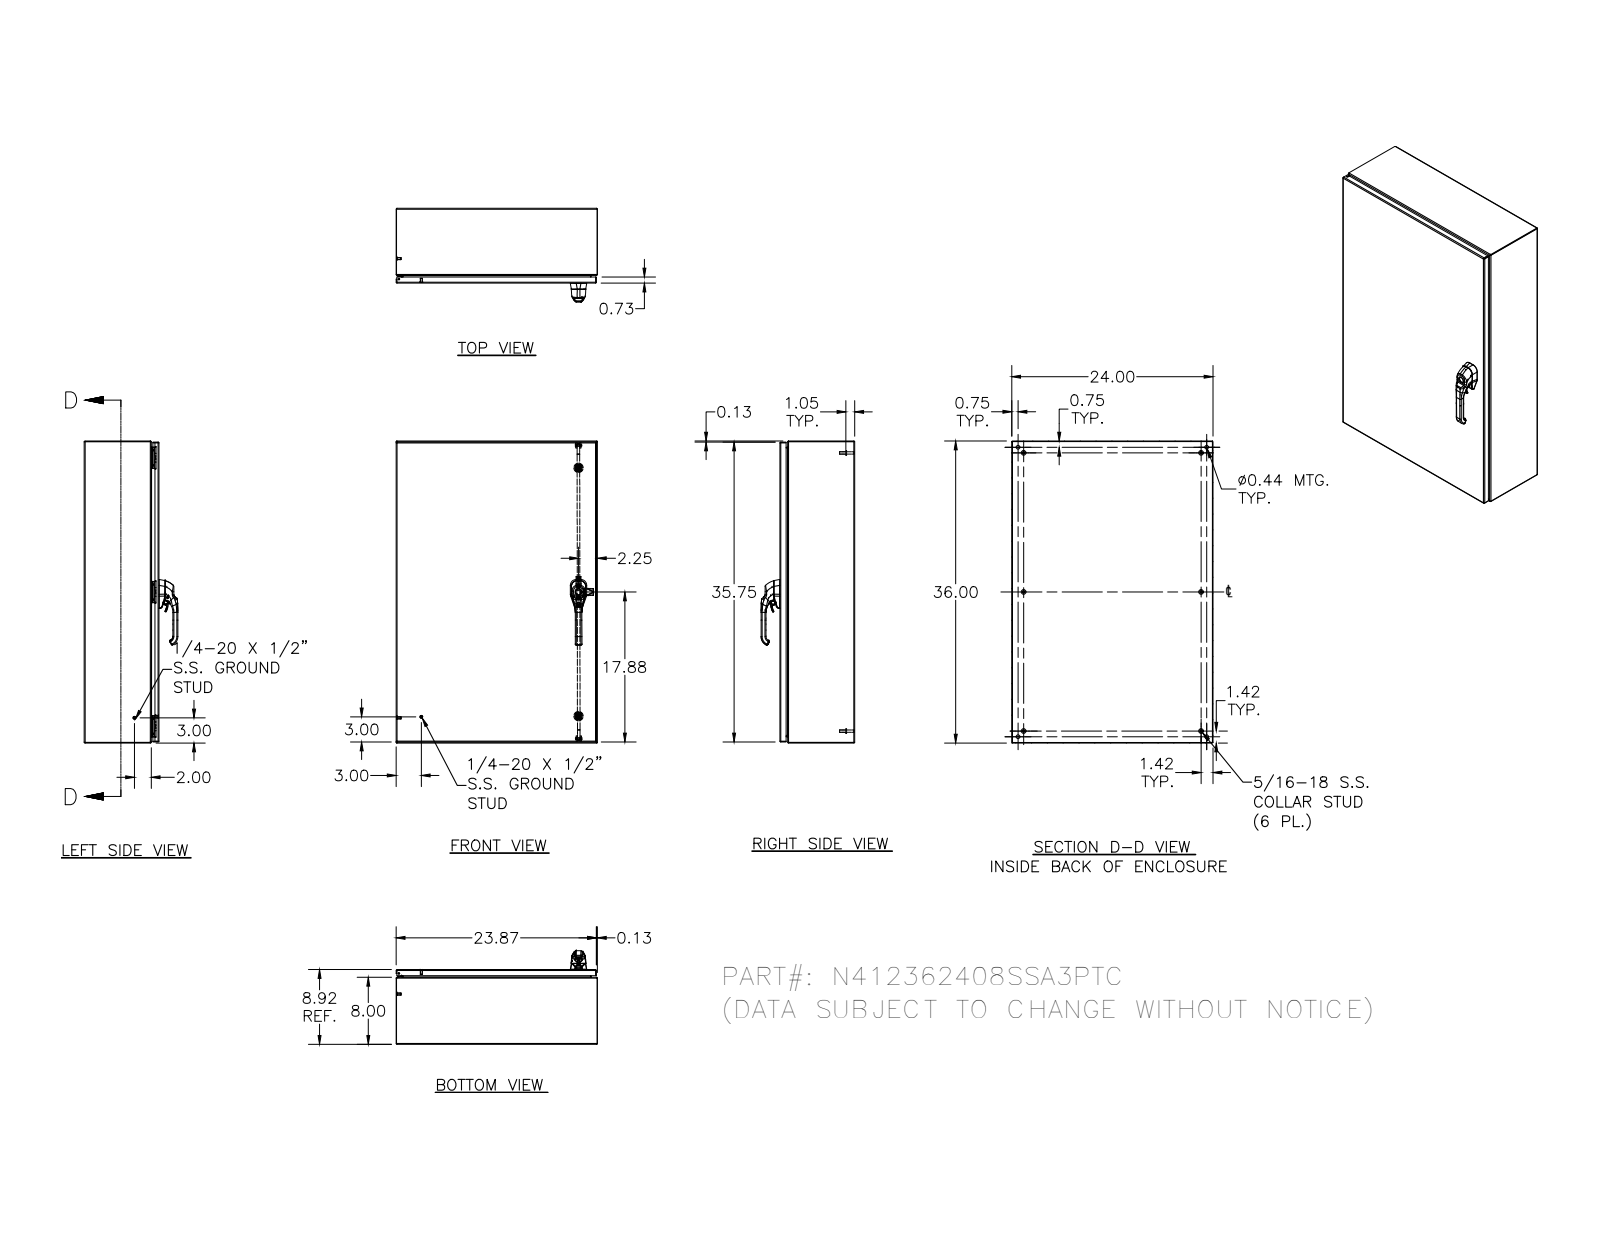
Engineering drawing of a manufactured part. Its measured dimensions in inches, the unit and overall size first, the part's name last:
Units: inches
Overall size (bounding box): 36 × 24 × 11.166
Round holes (diameter × count): ⌀0.188 ×7, ⌀0.093 ×6, ⌀0.152 ×6, ⌀0.167 ×6, ⌀0.172 ×6, ⌀0.165 ×5, ⌀0.197 ×4, ⌀0.437 ×4, ⌀0.156 ×3, ⌀0.213 ×3, ⌀0.106 ×2, ⌀0.16 ×2
Round bosses / shafts (diameter × count): ⌀0.25 ×14, ⌀0.563 ×6, ⌀0.36 ×6, ⌀0.32 ×6, ⌀0.3 ×6, ⌀0.275 ×6, ⌀0.256 ×6, ⌀0.236 ×6
Partial cylindrical surfaces — rounded edges, fillets, slot ends (radius × count): R0.02 ×178, R0.012 ×101, R0.05 ×38, R0.031 ×34, R0.016 ×26, R0.118 ×23, R0.019 ×21, R0.125 ×21
Main face-to-face distances: 0.074, 8.843, 8.769, 8.917, 23.926, 35.926, 23.852, 24, 36, 35.852
Hole centre spacings: 16, 15.996, 31.996, 16.008, 0.017, 0.66, 16.656, 22.869
Volume: 228.5 in³ · Surface area: 6 048 in²
Bodies: 74 solids, 3524 faces (1171 planar, 1297 cylindrical, 1056 other)
Part name (STEP PRODUCT): N412362408SSA3PTC; N412362408SSA3PTCBKP; N4123624SSA3PTCLID; HFW328176 (+8 more)
STEP written by: Autodesk Inventor 2011 (AUTOMOTIVE_DESIGN)
